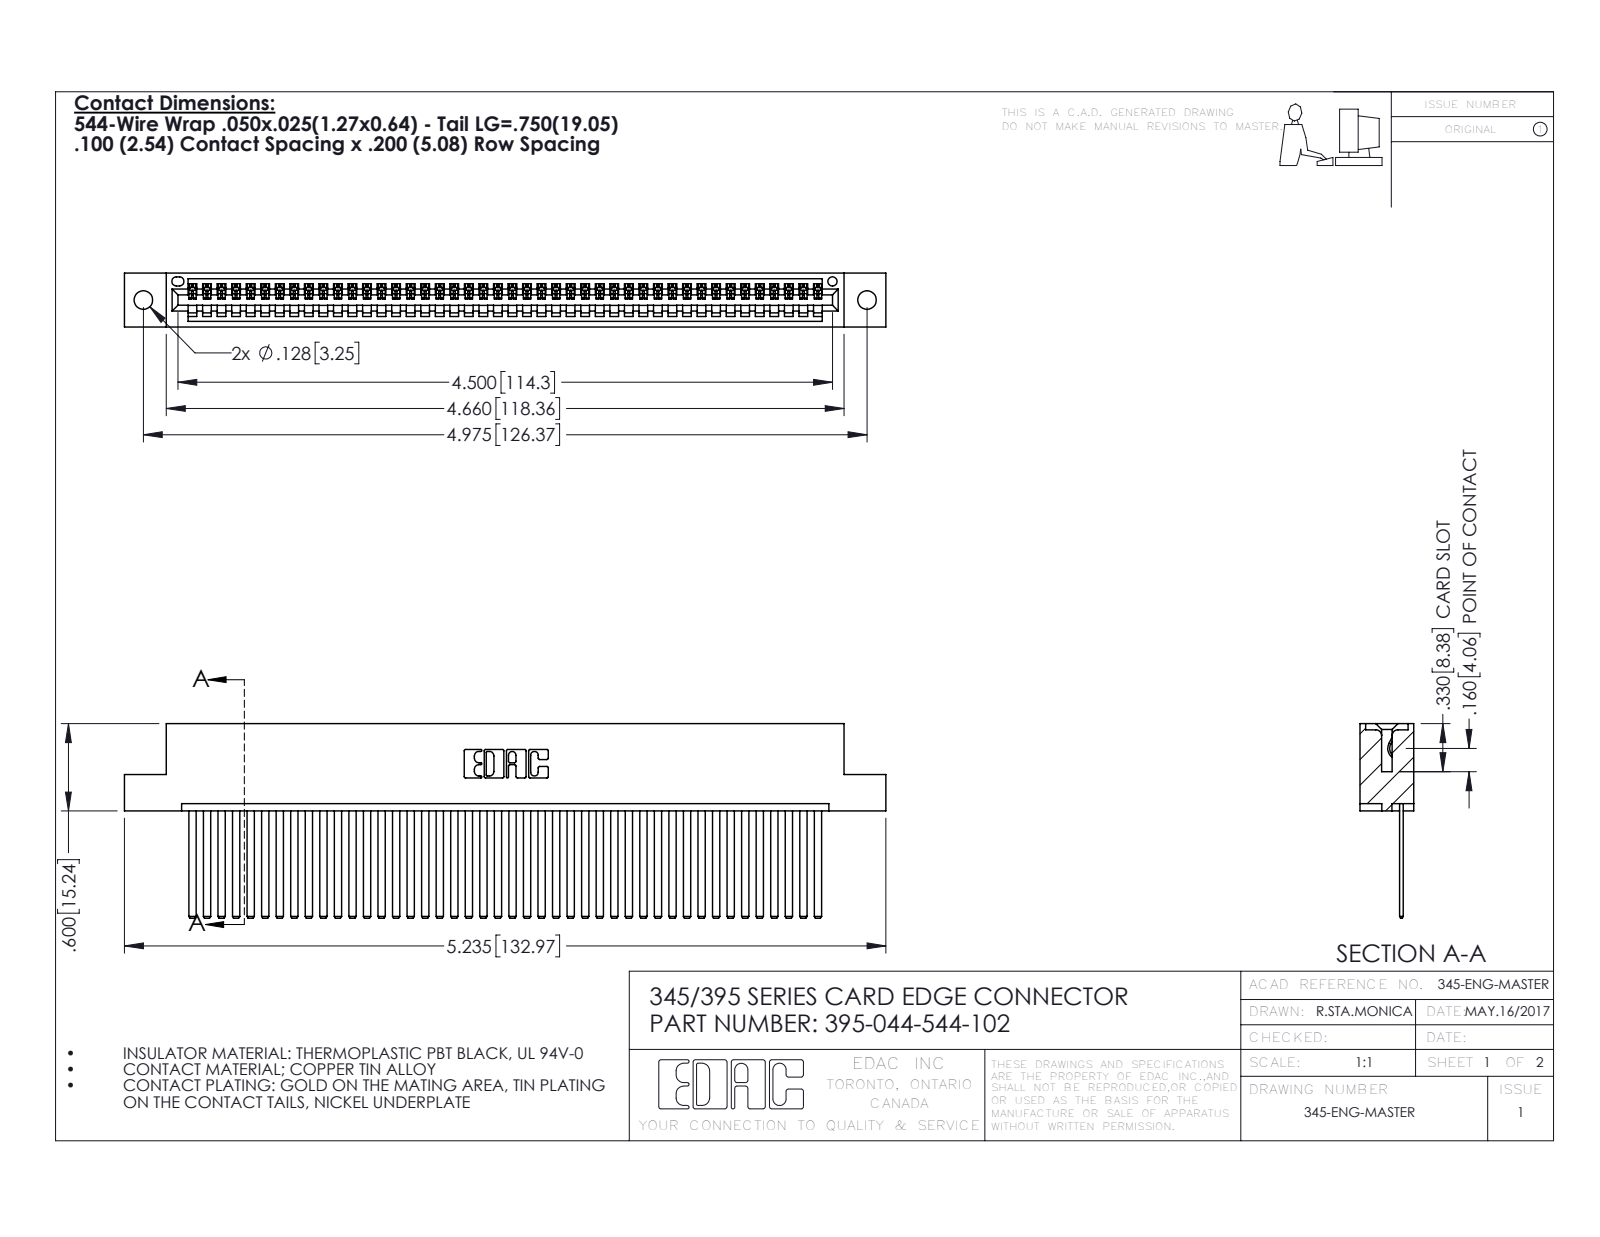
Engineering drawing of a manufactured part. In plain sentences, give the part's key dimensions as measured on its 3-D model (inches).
The part is named "395-044-544-102; 345-292-001_345-293-144; 345 Part_Flush Mounting Lugs - 0.128 Dia". Its 3-D file was written by "SolidWorks 2016 (CONFIG_CONTROL_DESIGN)". It is 45 solids with 2414 faces: 1664 planar, 750 cylindrical and 0 other. Overall it measures 5.235 by 1.337 by 0.37 inches. Its volume is 0.801 cubic inches and its surface area 29.01 square inches. Round holes: 2 of diameter 0.128, 1 of diameter 0.064. Partial cylindrical surfaces (rounded edges, fillets, slot ends): 88 of radius 0.006, 22 of radius 0.01, 6 of radius 0.007, 6 of radius 0.031, 3 of radius 0.026, 2 of radius 0.031, 2 of radius 0.04, 1 of radius 0.014. The main face-to-face distances are 0.072, 0.298, 0.025, 0.098, 0.272, 0.37, 0.2, 0.225, 0.149, 0.072. The hole center spacings are 0.27, 4.739, 4.975.
